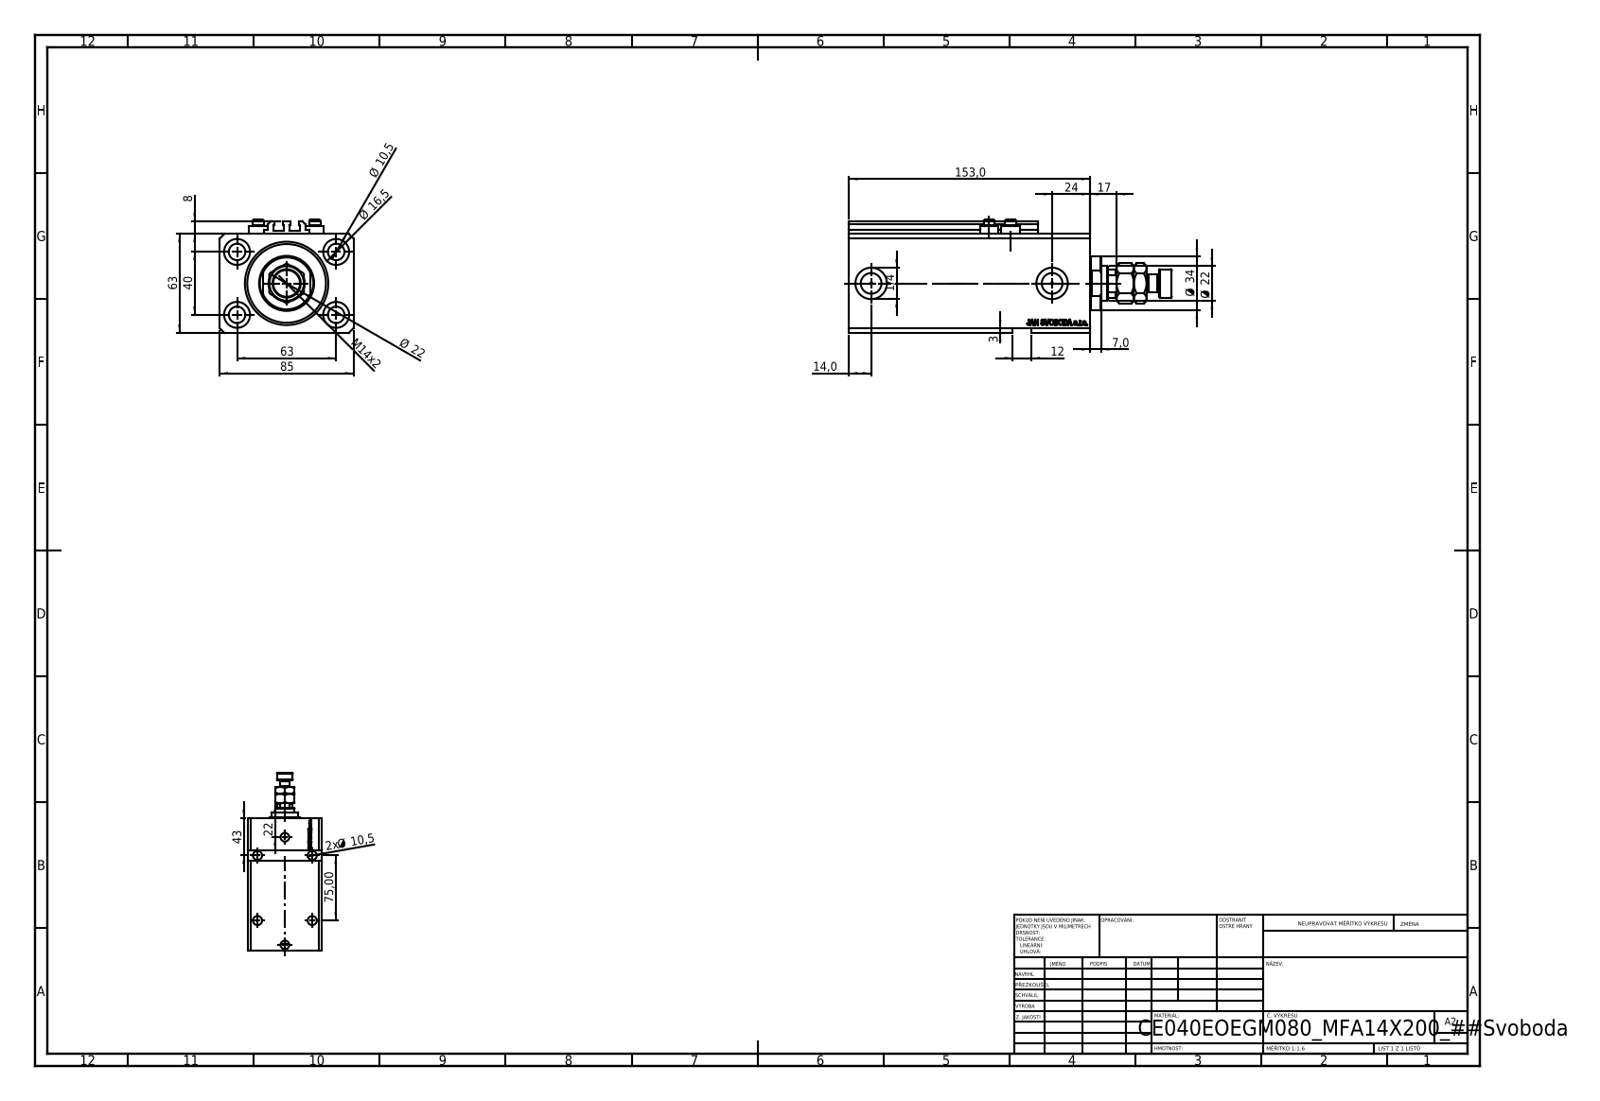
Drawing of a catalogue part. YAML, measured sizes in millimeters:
part_name: "V250CE_C_VCP; V250CE_VC_E; ALLEN BOLT V250CE; MFA (+1 more)"
step_written_by: "SolidWorks 2019 (CONFIG_CONTROL_DESIGN)"
units: millimeters
bodies: {solids: 9, faces: 1159, planar: 551, cylindrical: 150, other: 458}
overall_size: [205, 85, 72]
volume: 694537
surface_area: 144053
round_holes:
  - {diameter: 10.5, count: 8}
  - {diameter: 1.25, count: 4}
  - {diameter: 4, count: 4}
  - {diameter: 16.5, count: 4}
  - {diameter: 10, count: 2}
  - {diameter: 13.16, count: 2}
  - {diameter: 20, count: 2}
  - {diameter: 12.5, count: 1}
  - {diameter: 22, count: 1}
  - {diameter: 40, count: 1}
  - {diameter: 53, count: 1}
round_bosses_or_shafts:
  - {diameter: 11.6, count: 4}
  - {diameter: 7, count: 4}
  - {diameter: 34, count: 1}
  - {diameter: 18, count: 1}
  - {diameter: 11, count: 1}
partial_cylinders:
  - {radius: 0.2, count: 10}
  - {radius: 10.5, count: 1}
face_to_face_distances: [63, 85, 17, 153, 136, 11.4, 124.6, 141.6, 65, 3]
hole_center_spacings: [37.31, 63, 13.6, 15.4, 24.96, 33.62, 36, 37.86]
